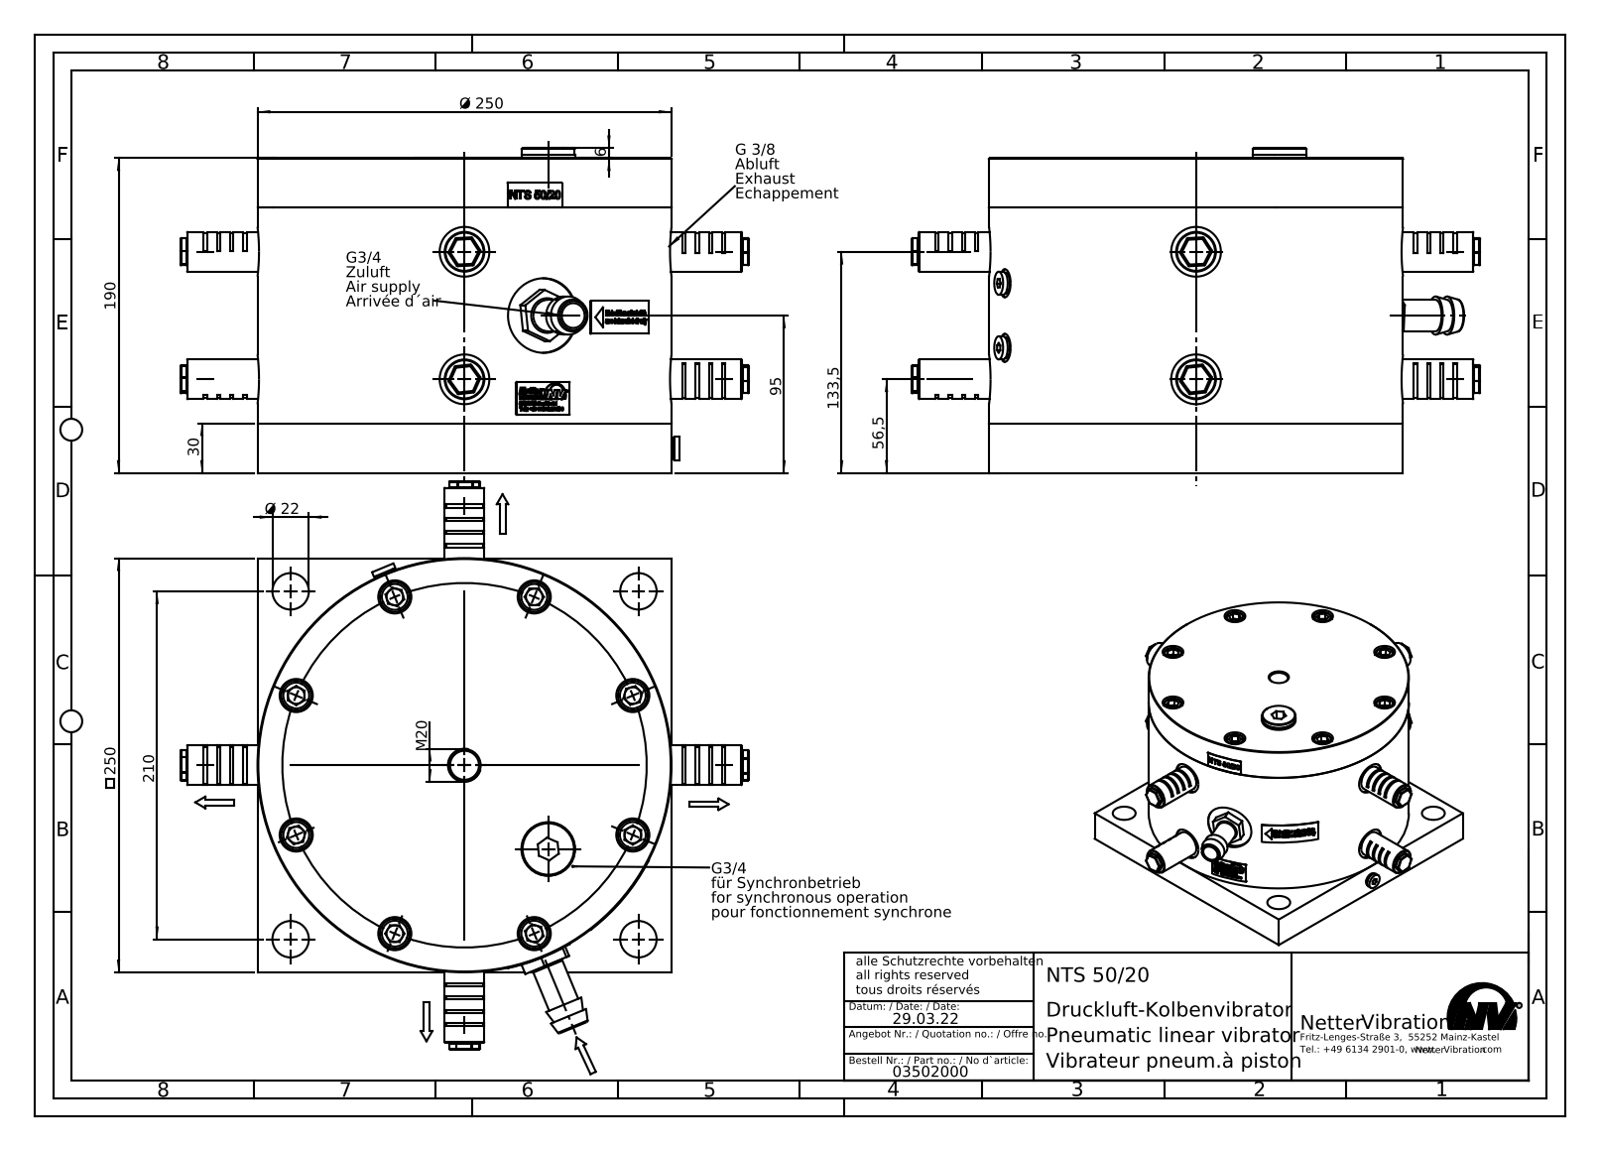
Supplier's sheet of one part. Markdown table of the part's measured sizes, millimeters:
| quantity | value |
| --- | --- |
| part name | NTS 50-20 Kolbenvibrator #03502000 |
| STEP written by | SolidWorks 2015 (AUTOMOTIVE_DESIGN) |
| units | millimeters |
| bodies | 35 solids, 1644 faces (539 planar, 679 cylindrical, 426 other) |
| overall size | 343 × 343 × 196 |
| volume | 9 801 000 mm³ |
| surface area | 654 098 mm² |
| round holes (diameter × count) | 10.2 × 8, 12.5 × 8, 20 × 8, 14.95 × 4, 22 × 4, 30 × 4, 8.57 × 3, 2 × 2, 6 × 2, 24.12 × 2, 1 × 1, 10 × 1 |
| round bosses / shafts (diameter × count) | 18 × 8, 12 × 8, 24 × 4, 16.66 × 4, 250 × 1, 32.4 × 1, 32 × 1, 26.44 × 1 |
| partial cylindrical surfaces (radius × count) | 0.5 × 132, 11 × 4, 125.2 × 1 |
| main face-to-face distances | 30, 160, 130, 190, 250, 1.5, 248.5, 13, 17, 177 |
| hole center spacings | 62.99, 110, 147.14, 155.57, 203.26, 215.99, 253.64, 19.5 |
